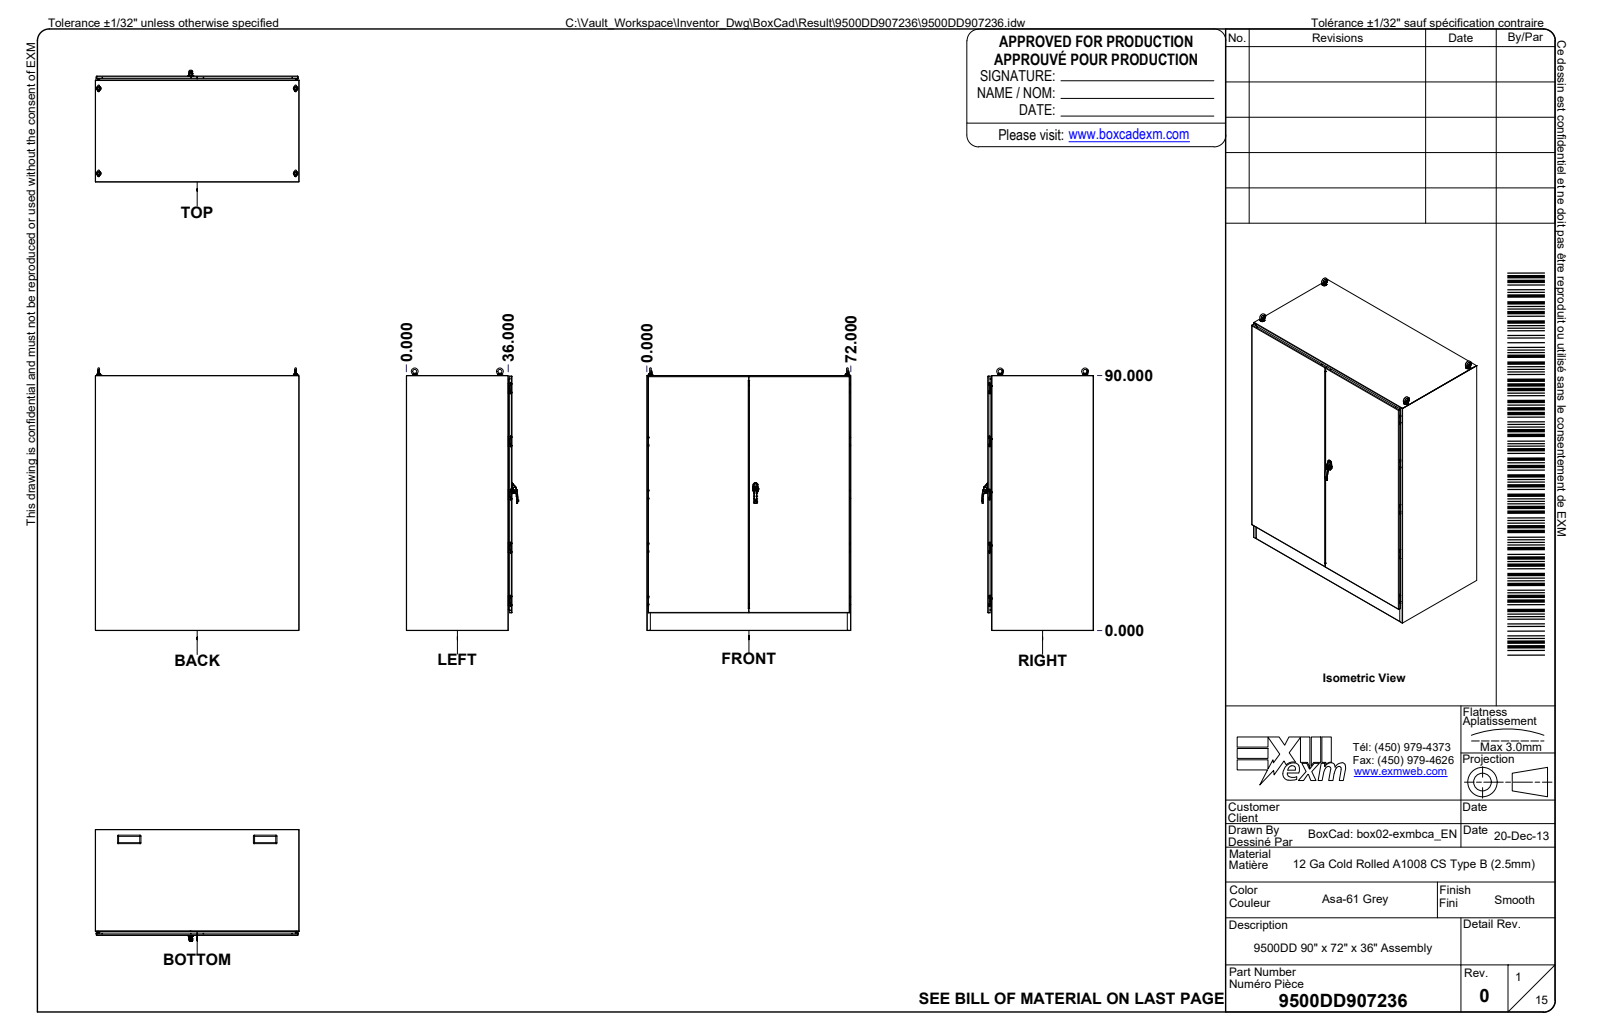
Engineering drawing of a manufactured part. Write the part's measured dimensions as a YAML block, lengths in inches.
part_name: "9500DD907236; 9500DD907236B; 9500DD907236B-P; 9500DD907236LS-P (+8 more)"
step_written_by: "Autodesk Inventor 2024 (AUTOMOTIVE_DESIGN)"
units: inches
bodies: {solids: 335, faces: 41594, planar: 14514, cylindrical: 10880, other: 16200}
overall_size: [92.638, 72, 39.422]
volume: 2656
surface_area: 60584
round_holes:
  - {diameter: 0.177, count: 432}
  - {diameter: 0.03, count: 41}
  - {diameter: 0.201, count: 26}
  - {diameter: 0.043, count: 20}
  - {diameter: 0.167, count: 16}
  - {diameter: 0.315, count: 15}
  - {diameter: 0.512, count: 12}
  - {diameter: 0.203, count: 10}
  - {diameter: 0.339, count: 8}
  - {diameter: 0.341, count: 8}
  - {diameter: 0.591, count: 8}
  - {diameter: 0.469, count: 7}
round_bosses_or_shafts:
  - {diameter: 0.272, count: 312}
  - {diameter: 0.232, count: 43}
  - {diameter: 0.03, count: 41}
  - {diameter: 0.039, count: 39}
  - {diameter: 0.289, count: 20}
  - {diameter: 0.177, count: 20}
  - {diameter: 0.39, count: 16}
  - {diameter: 0.051, count: 12}
partial_cylinders:
  - {radius: 0.02, count: 1344}
  - {radius: 0.039, count: 511}
  - {radius: 0.012, count: 292}
  - {radius: 0.031, count: 252}
  - {radius: 0.008, count: 250}
  - {radius: 0.062, count: 204}
  - {radius: 0.01, count: 183}
  - {radius: 0.01, count: 161}
face_to_face_distances: [0.089, 37.255, 71.911, 37.166, 37.344, 89.911, 71.822, 72, 89.822, 90]
hole_center_spacings: [18.75, 37.5, 1, 56.25, 17.75, 19.75, 36.5, 38.5]
